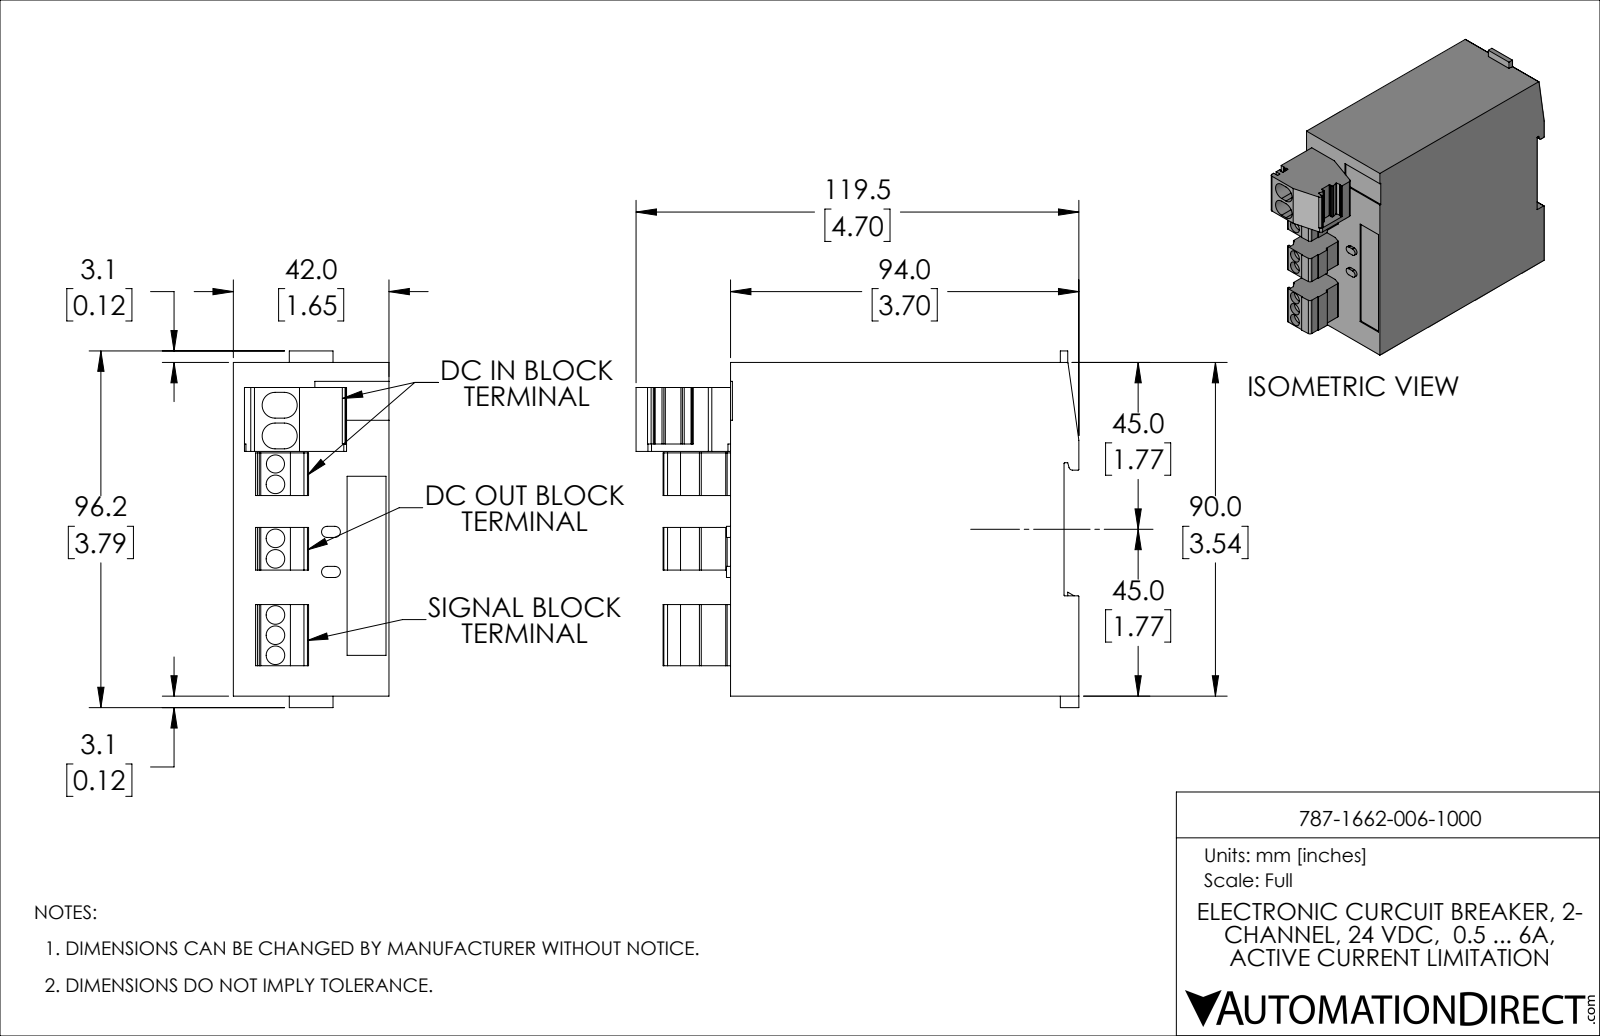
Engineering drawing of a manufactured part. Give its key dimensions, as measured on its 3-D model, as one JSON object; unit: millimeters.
{"part_name": "787-1662", "step_written_by": "PARTsolutions (CONFIG_CONTROL_DESIGN)", "units": "millimeters", "bodies": {"solids": 1, "faces": 204, "planar": 153, "cylindrical": 51, "other": 0}, "overall_size": [119.5, 96.2, 42], "volume_mm3": 366890, "surface_area_mm2": 39175, "partial_cylinders_radius": [[0.2, 17], [1, 7], [0.4, 4], [1.5, 4], [0.3, 2], [0.49, 2], [2, 1]], "face_to_face_distances": [42, 90, 4, 94, 24, 3, 0.5, 93.5, 89.5, 66]}
